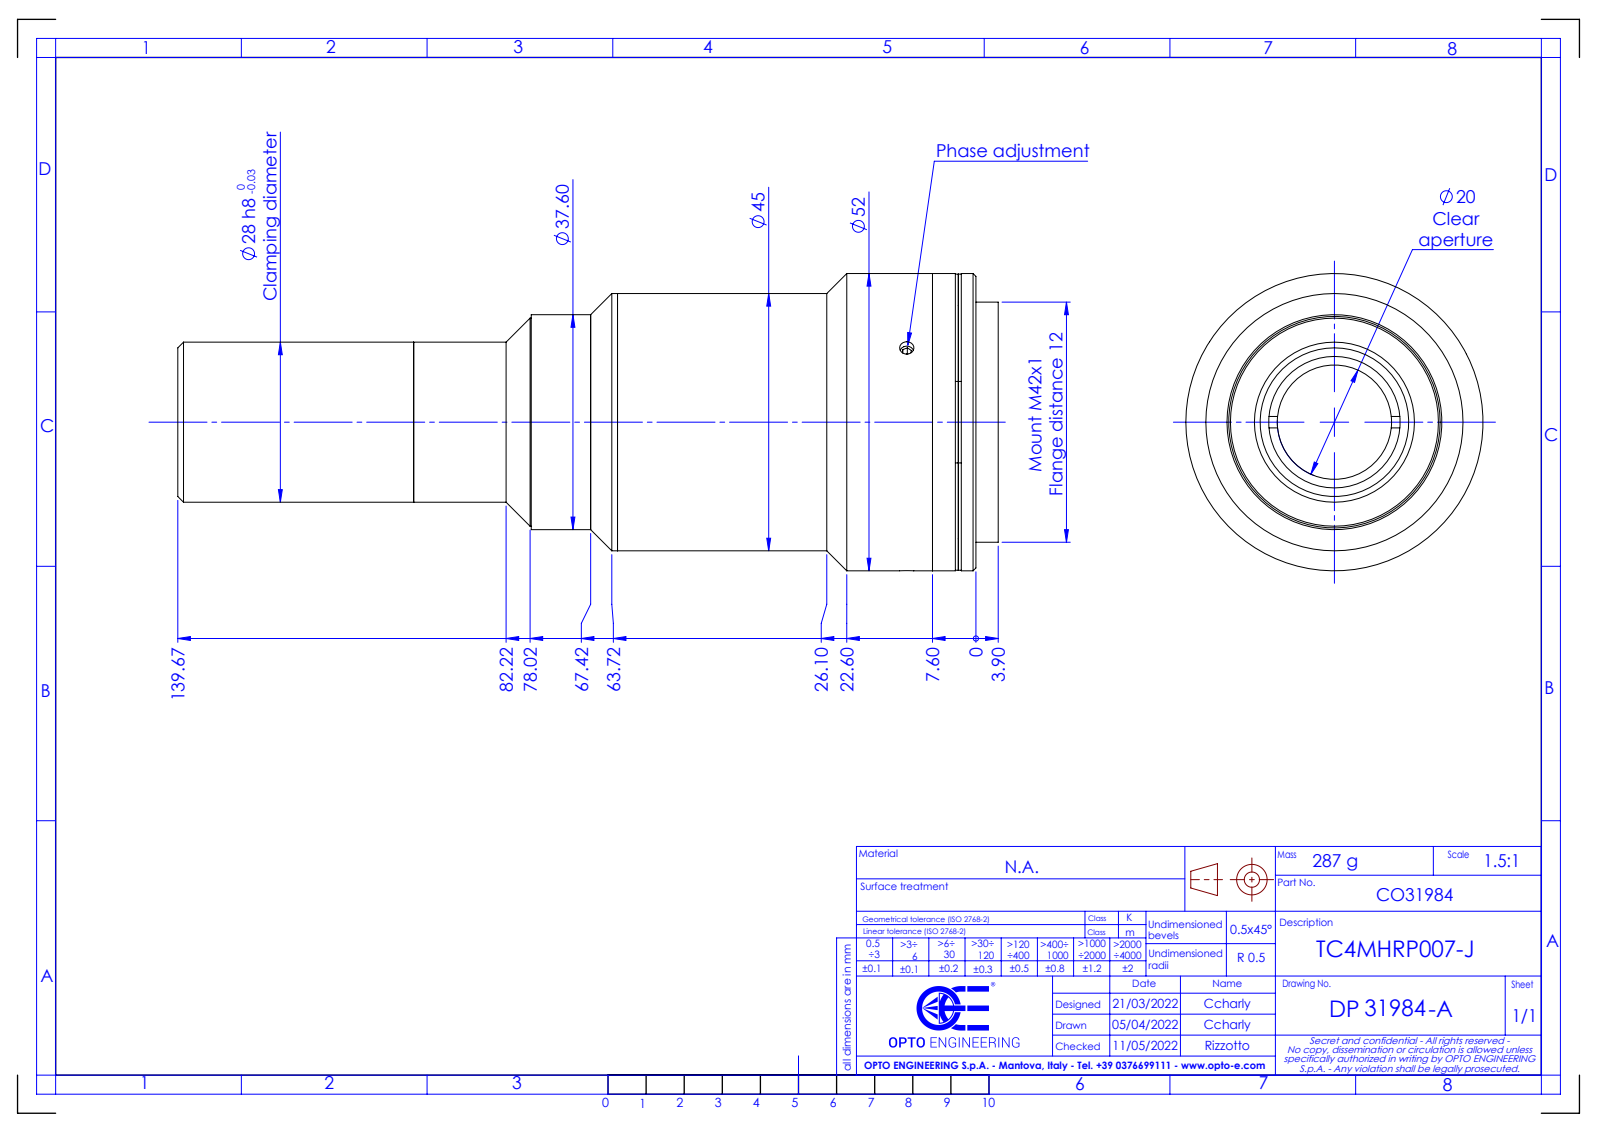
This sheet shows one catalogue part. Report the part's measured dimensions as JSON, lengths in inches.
{"part_name": "DP31984-A_TC4MHRP007-J", "step_written_by": "SolidWorks 2021 (CONFIG_CONTROL_DESIGN)", "units": "inches", "bodies": {"solids": 0, "faces": 99, "planar": 39, "cylindrical": 38, "other": 22}, "overall_size": [5.652, 2.047, 2.047], "round_holes": [[0.098, 3], [0.787, 1], [0.906, 1], [1.496, 1], [1.614, 1]], "round_bosses_or_shafts": [[2.047, 1], [2.039, 1], [1.772, 1], [1.654, 1], [1.48, 1], [1.433, 1], [1.102, 1]], "face_to_face_distances": [0.02, 0.021, 0.198, 0.157, 0.041, 0.299, 0.142, 0.101, 0.177, 0.122]}
